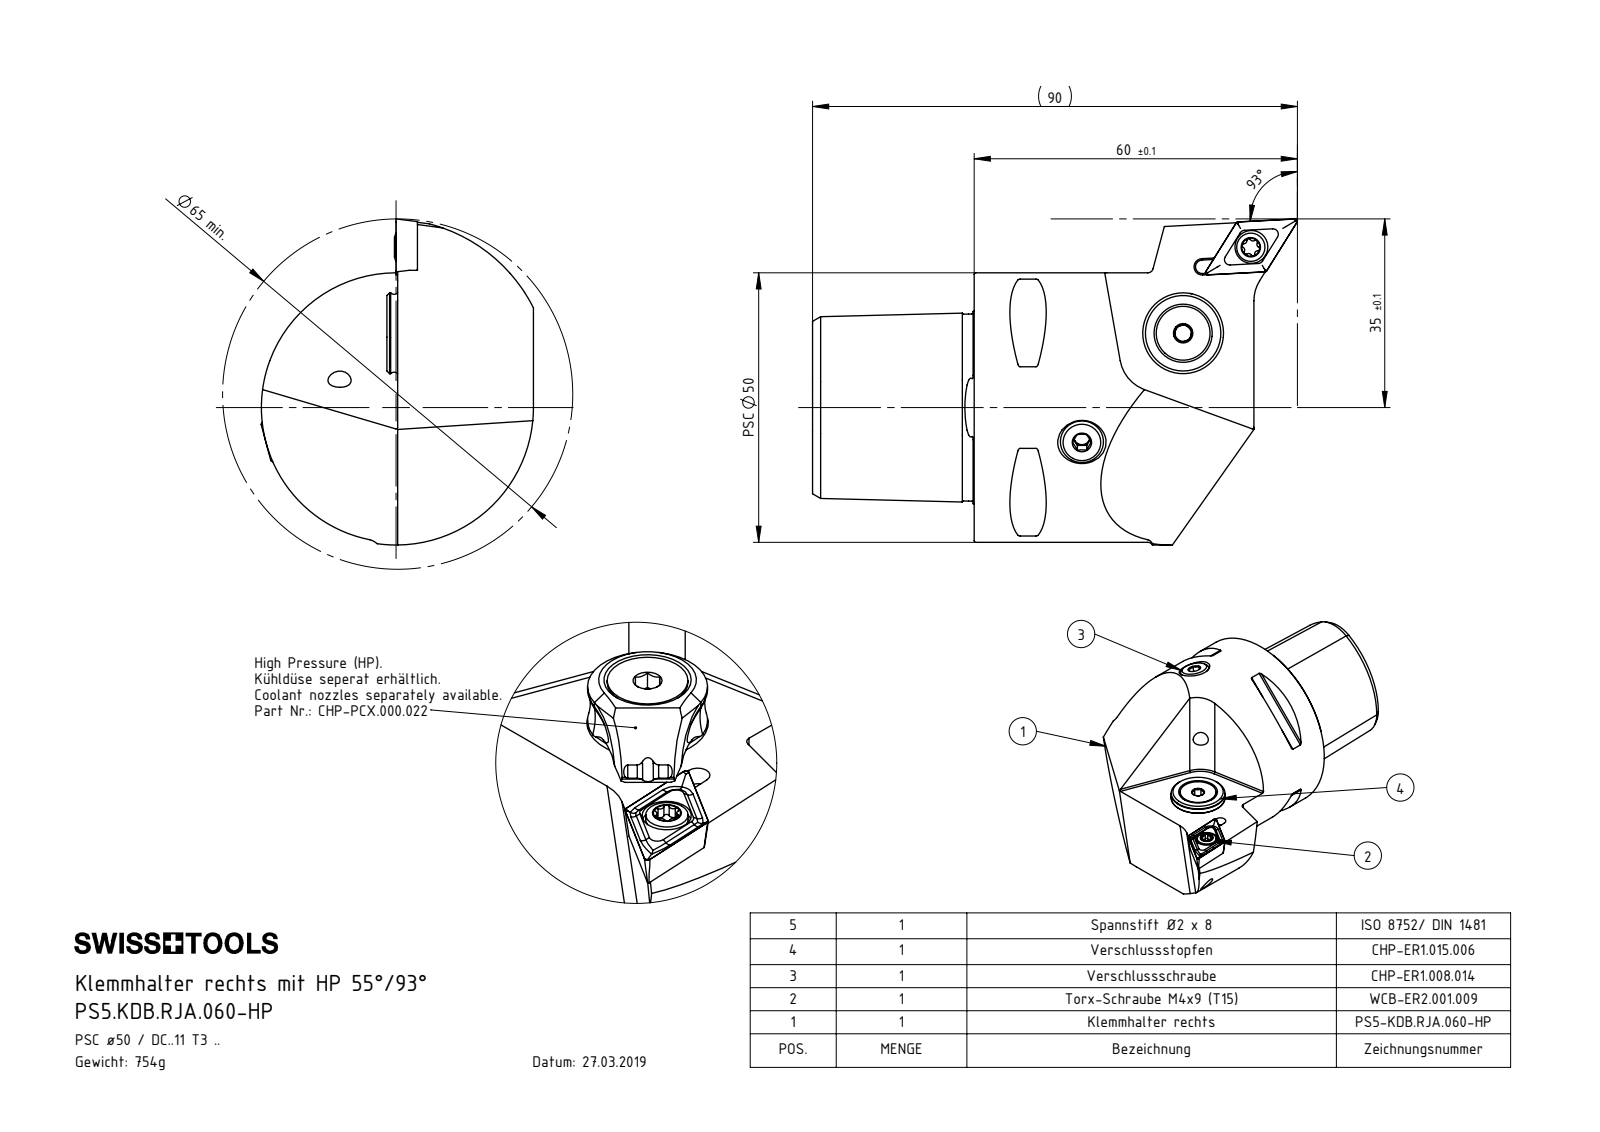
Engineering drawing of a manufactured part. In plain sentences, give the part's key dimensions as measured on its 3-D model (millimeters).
The part is named "CHP-ER1.015.006; ISO 8752 2x8; CHP-ER1.015.006_A; DCMT11T304 (+6 more)". Its 3-D file was written by "SolidWorks 2017 (AUTOMOTIVE_DESIGN)". It is 8 solids with 375 faces: 91 planar, 100 cylindrical and 184 other. Overall it measures 90.01 by 60.5 by 50.55 millimeters. Its volume is 95 695 cubic millimeters and its surface area 21 955 square millimeters. Round holes: 3 of diameter 4.2, 2 of diameter 6.1, 1 of diameter 1.2, 1 of diameter 2, 1 of diameter 2.5, 1 of diameter 3, 1 of diameter 3.3, 1 of diameter 4, 1 of diameter 4.4, 1 of diameter 5, 1 of diameter 5.2, 1 of diameter 7. Round bosses or shafts: 1 of diameter 50, 1 of diameter 15, 1 of diameter 13.4, 1 of diameter 10, 1 of diameter 8, 1 of diameter 5.5, 1 of diameter 5.25, 1 of diameter 5. Partial cylindrical surfaces (rounded edges, fillets, slot ends): 10 of radius 0.5, 6 of radius 0.34, 6 of radius 0.59, 2 of radius 7, 1 of radius 1.25, 1 of radius 4, 1 of radius 25.5, 1 of radius 30. The main face-to-face distances are 30, 25.2, 20.7, 4.5, 19.18, 21.53, 0.83, 3.67, 44.4, 10. The hole center spacings are 4.49, 16.67, 16.79, 20.3, 20.42, 26, 30.13, 32.81.
